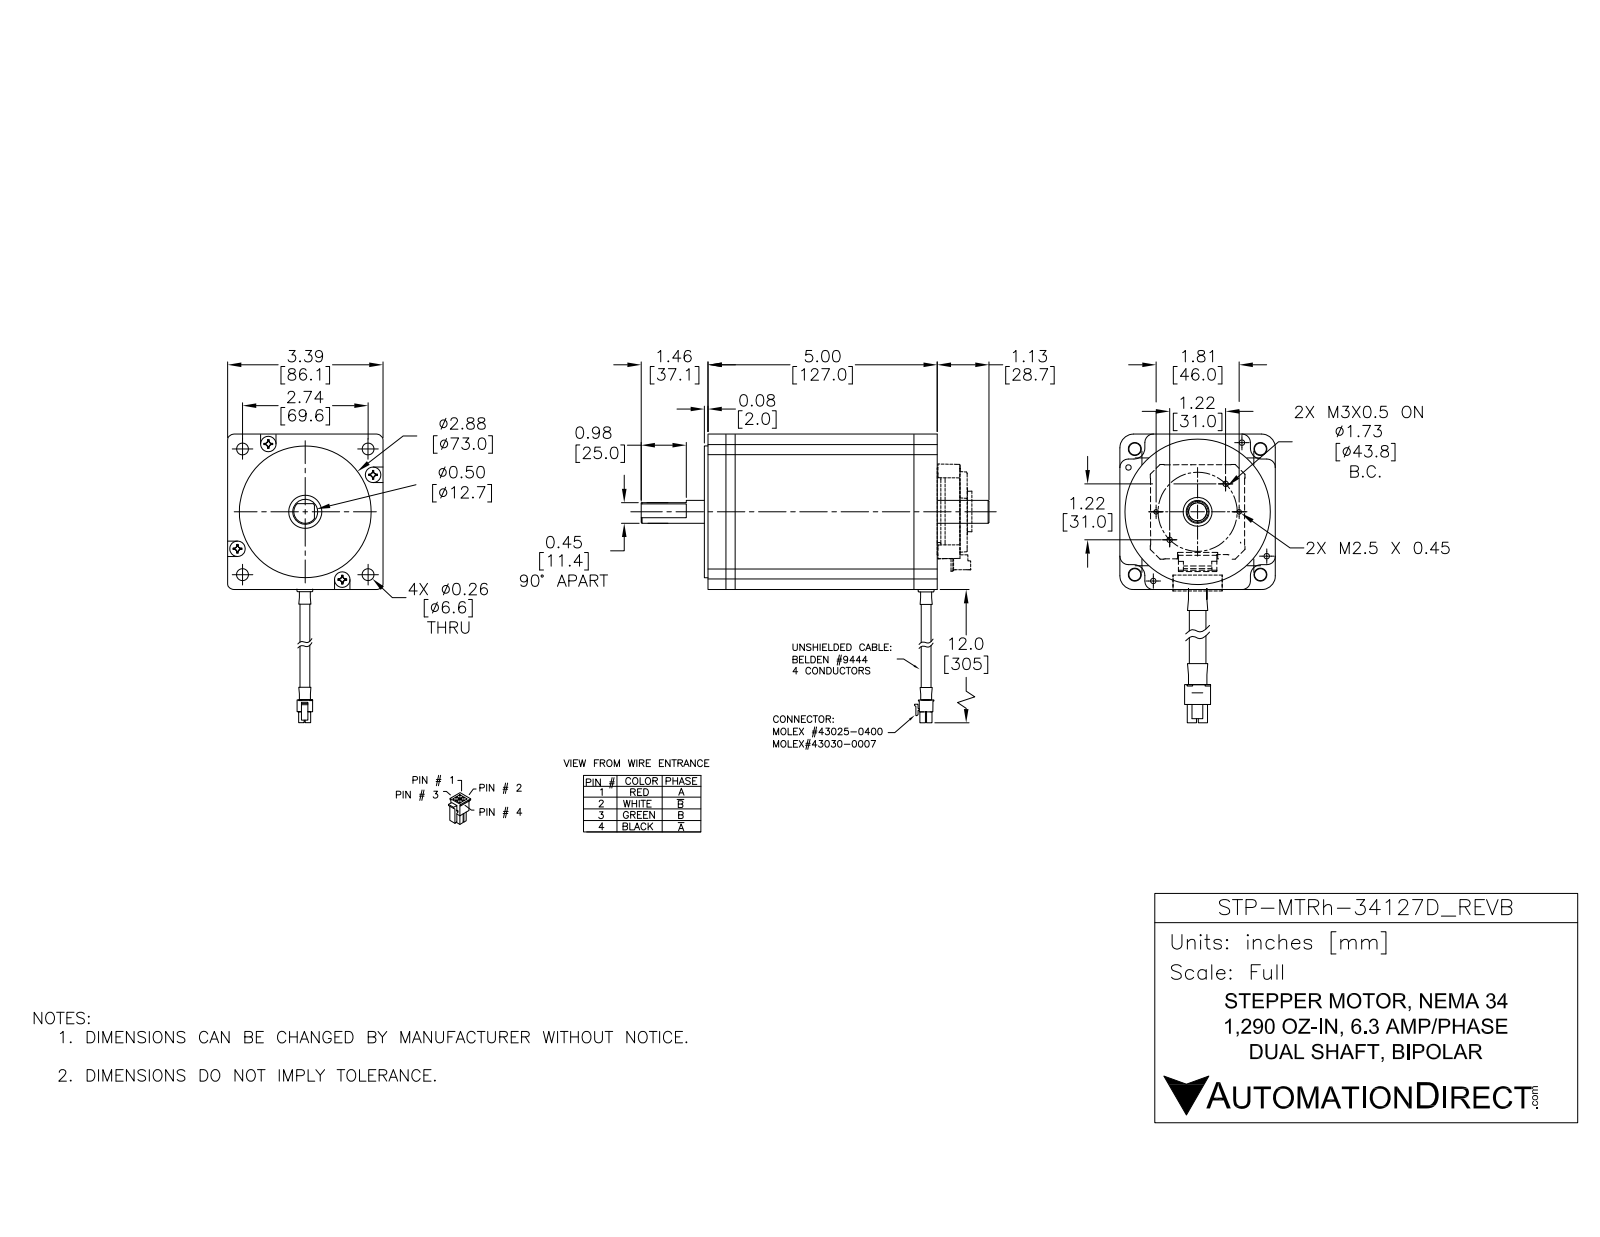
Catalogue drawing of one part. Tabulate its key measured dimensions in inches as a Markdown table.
| quantity | value |
| --- | --- |
| part name | 8718L-04PD-12RO Coord fXT |
| STEP written by | SolidWorks 2017 (AUTOMOTIVE_DESIGN) |
| units | inches |
| bodies | 1 solid, 205 faces (107 planar, 71 cylindrical, 27 other) |
| overall size | 7.551 × 4.386 × 3.39 |
| volume | 52.19 in³ |
| surface area | 95.1 in² |
| round holes (diameter × count) | 0.118 × 6, 0.26 × 4, 0.098 × 2, 0.63 × 1, 1.89 × 1, 3.169 × 1 |
| round bosses / shafts (diameter × count) | 0.213 × 4, 2.875 × 1, 1.339 × 1, 0.5 × 1, 0.276 × 1 |
| partial cylindrical surfaces (radius × count) | 0.185 × 8, 0.167 × 4, 0.236 × 4, 0.299 × 4 |
| main face-to-face distances | 3.39, 5.035, 0.543, 2.846, 4.957, 0.079, 4.961, 5.039, 2.303, 4.902 |
| hole center spacings | 0.426, 1.446, 1.791, 1.937, 2.121, 2.341, 2.533, 2.657 |
